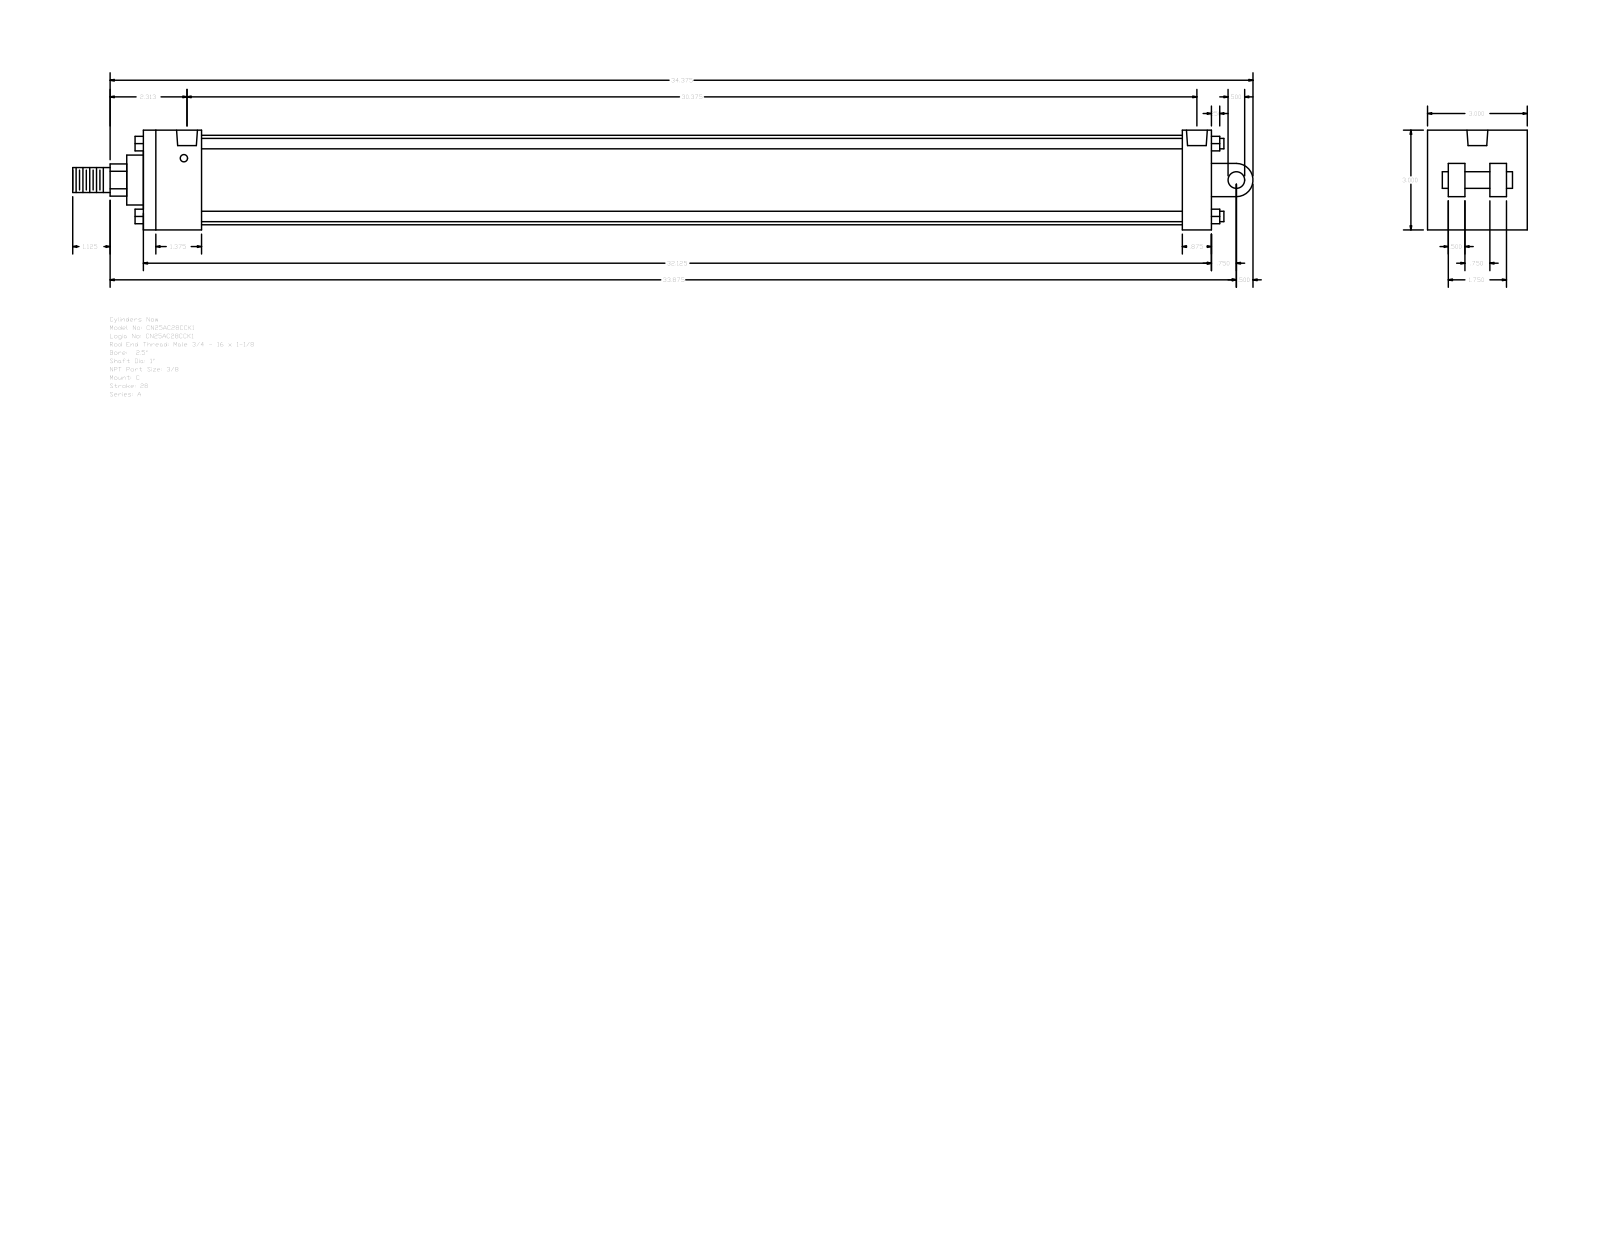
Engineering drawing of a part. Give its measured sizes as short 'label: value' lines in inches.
name: A_C__0250_1
written by: GSSL Pune (CONFIG_CONTROL_DESIGN)
unit: in
bodies: 0 solids, 135 faces (102 planar, 33 cylindrical, 0 other)
size: 35.5 × 3 × 3
holes: 4× ⌀0.219, 2× ⌀0.627
bosses: 4× ⌀0.313, 1× ⌀2.69, 1× ⌀1.5, 1× ⌀1, 1× ⌀0.75, 1× ⌀0.5
rounds: 1× R0.484, 1× R0.5
face distances: 3, 32.125, 0.5, 1.75, 31.25, 29.5, 30.375, 0.875, 0.625, 1
hole spacings: 0.094, 30.469, 30.562, 30.375
